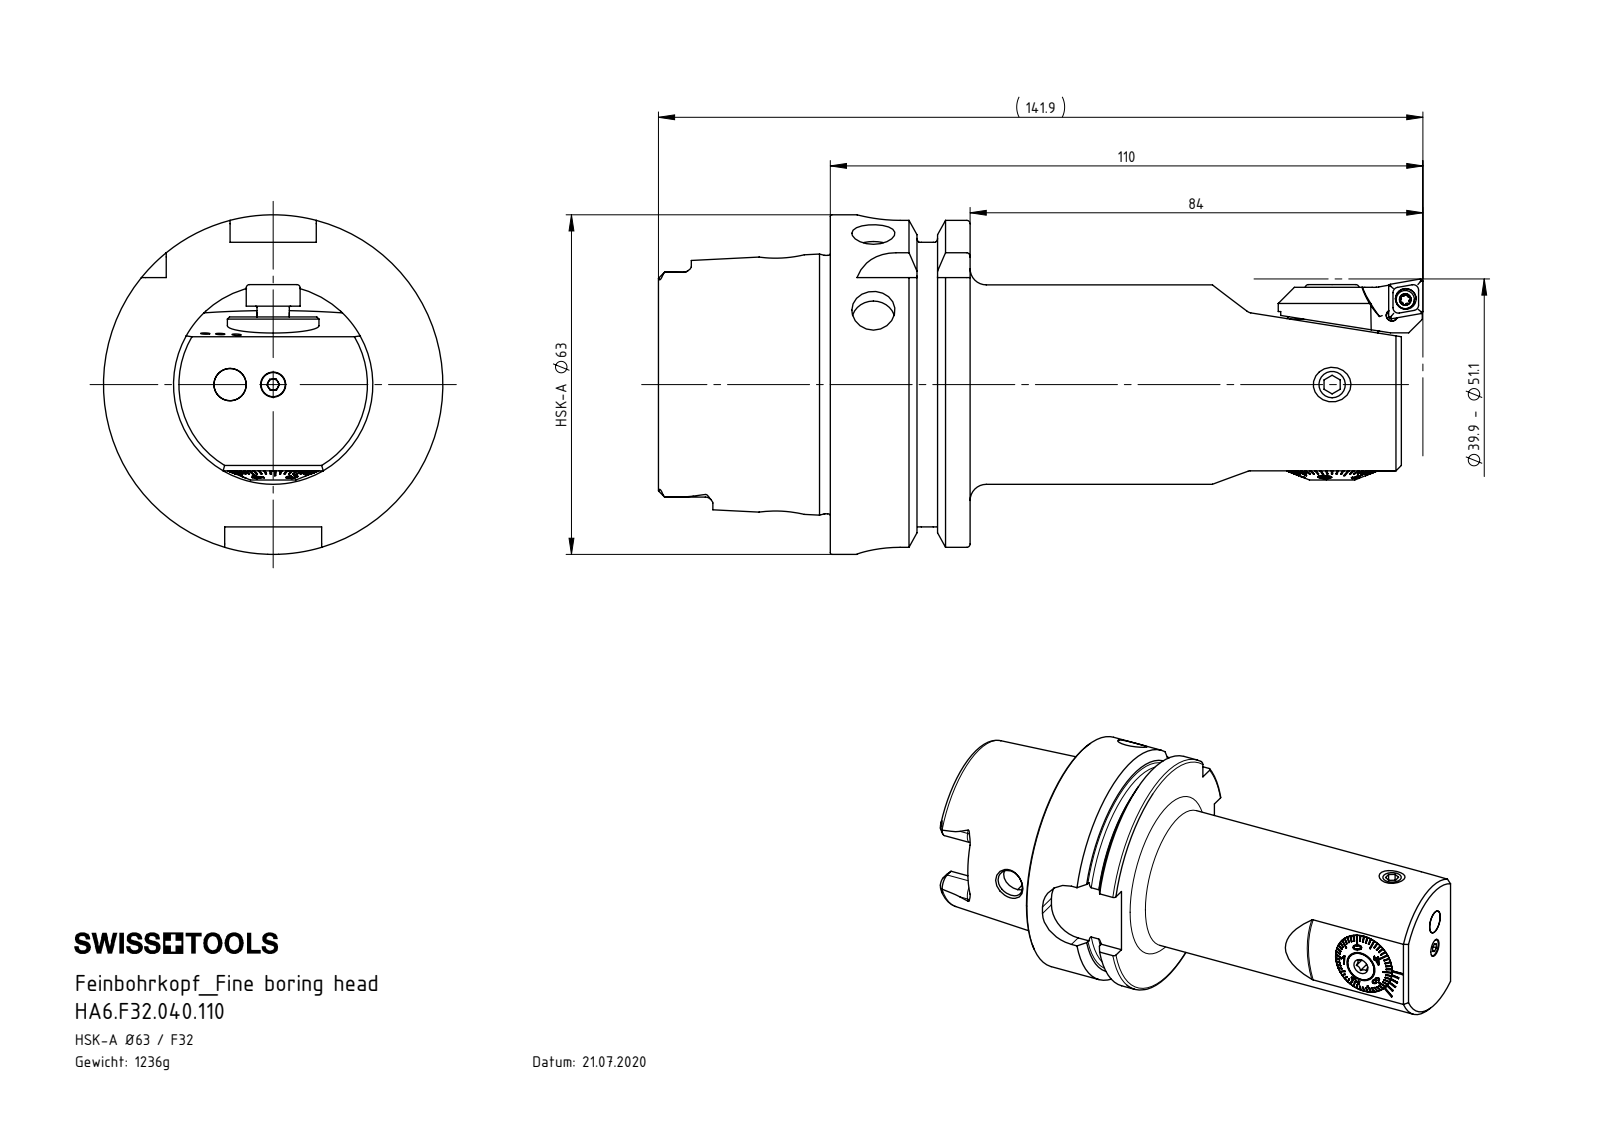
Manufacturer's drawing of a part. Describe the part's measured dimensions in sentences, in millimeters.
The part is named "HA6.F32.AA4.110; F32-BG3.006.026_A; F32-BG1.010.006_A; F32-BG1.DA3.017_A_Aktuell 0.6.2014-Mx1.3 (+8 more)". Its 3-D file was written by "SolidWorks 2017 (AUTOMOTIVE_DESIGN)". It is 13 solids with 643 faces: 348 planar, 91 cylindrical and 204 other. Overall it measures 137.9 by 63 by 63 millimeters. Its volume is 158 170 cubic millimeters and its surface area 41 131 square millimeters. Round holes: 3 of diameter 1.5, 2 of diameter 3.3, 2 of diameter 5, 2 of diameter 8, 2 of diameter 8.5, 1 of diameter 2.05, 1 of diameter 2.7, 1 of diameter 2.9, 1 of diameter 3, 1 of diameter 4.2, 1 of diameter 6, 1 of diameter 7. Round bosses or shafts: 2 of diameter 6, 1 of diameter 63, 1 of diameter 54.95, 1 of diameter 47.94, 1 of diameter 37, 1 of diameter 17, 1 of diameter 16.98, 1 of diameter 16.85. Partial cylindrical surfaces (rounded edges, fillets, slot ends): 10 of radius 1.4, 4 of radius 2.88, 4 of radius 8, 3 of radius 0.5, 2 of radius 1.75, 2 of radius 2, 1 of radius 2.1, 1 of radius 3.2. The main face-to-face distances are 25.95, 106, 80.05, 16, 9.95, 96.05, 31.9, 41.85, 57.85, 137.9. The hole center spacings are 8, 8.72, 86.15, 93.16, 102.15.
